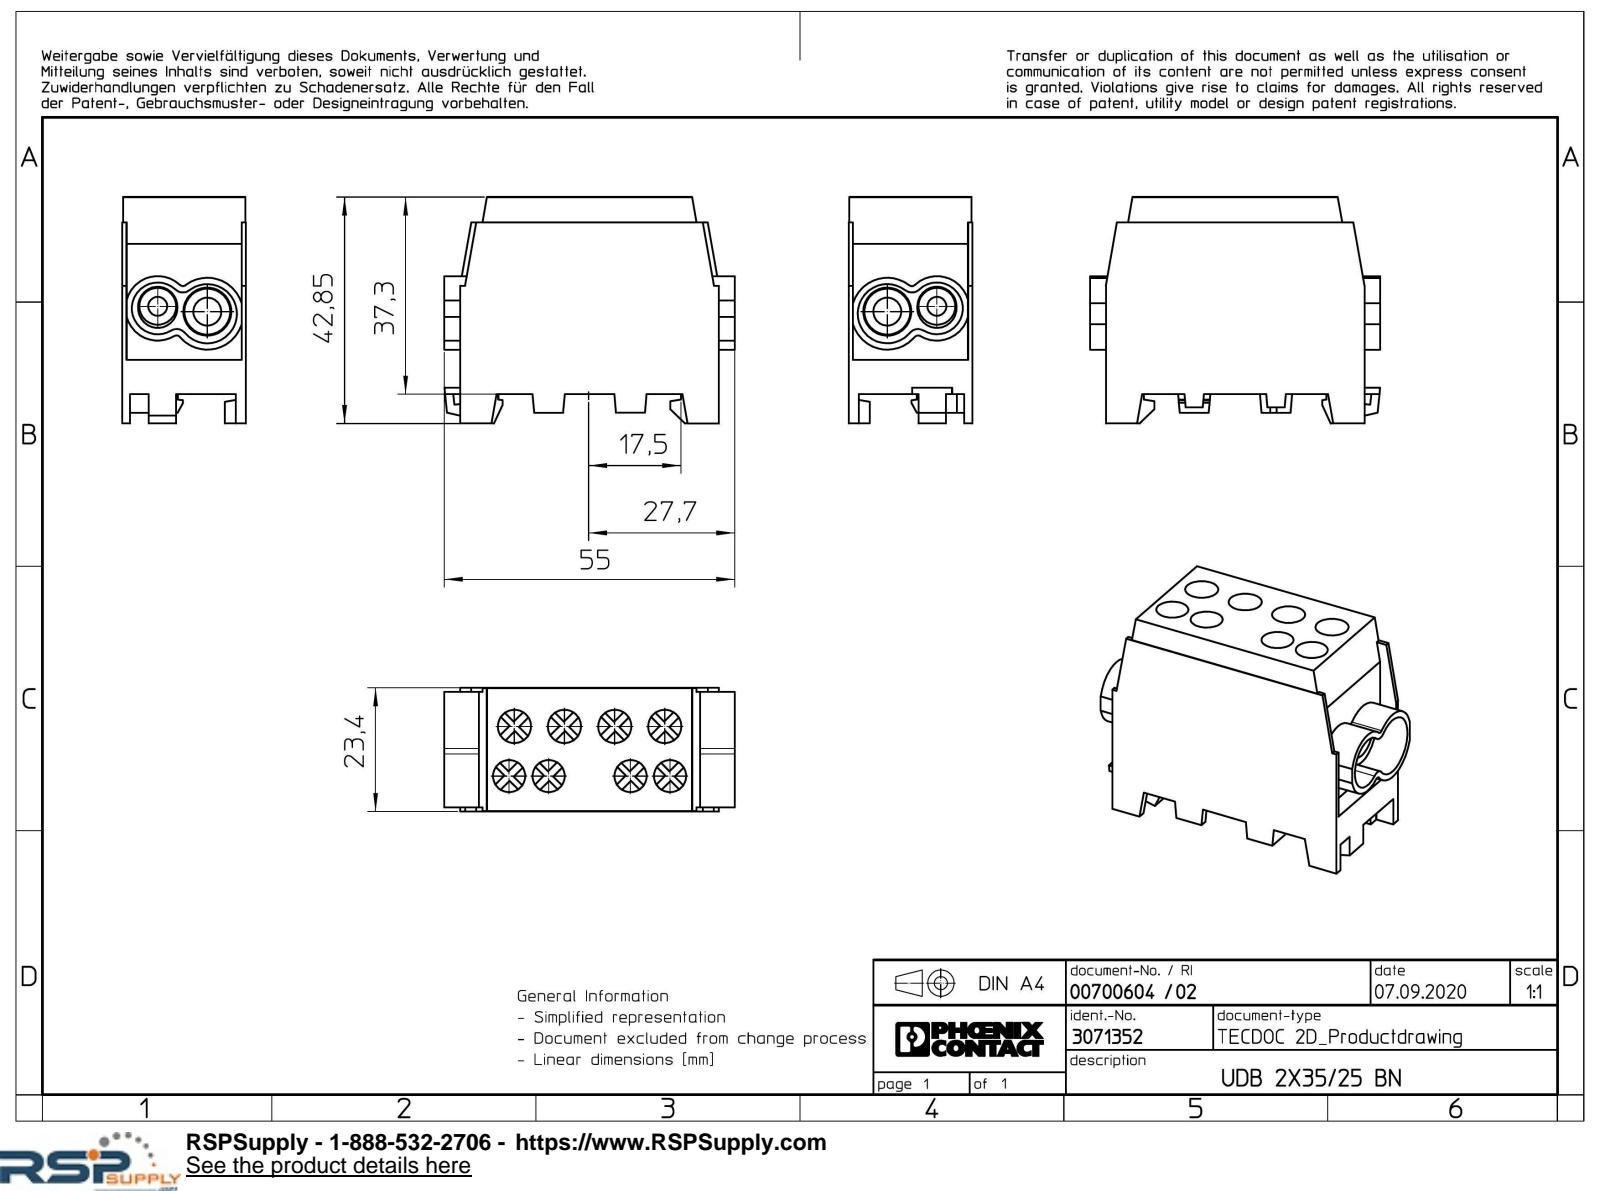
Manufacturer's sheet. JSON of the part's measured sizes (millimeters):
{"part_name": "UDB_2x35_25_BN-select", "step_written_by": "Creo Elements/Direct Modeling 20.1A 29-Sep-2018 (C) Parametric Technology GmbH (AUTOMOTIVE_DESIGN)", "units": "millimeters", "bodies": {"solids": 1, "faces": 275, "planar": 209, "cylindrical": 52, "other": 14}, "overall_size": [55, 42.85, 23.4], "volume_mm3": 33976, "surface_area_mm2": 13197, "round_holes": [[6.1, 4], [6.3, 4], [7, 1], [8.7, 1], [9.1, 1]], "partial_cylinders_radius": [[0.8, 2], [2, 2], [3.7, 2], [4.9, 1], [5.6, 1], [6.1, 1], [6.8, 1]], "face_to_face_distances": [23.4, 37.3, 3.5, 45.5, 23.3, 0.7, 0.8, 6.5, 22.6, 22.5], "hole_center_spacings": [9.45, 7.5, 11.43, 15.64, 22.1, 23, 23.92, 30.96]}
